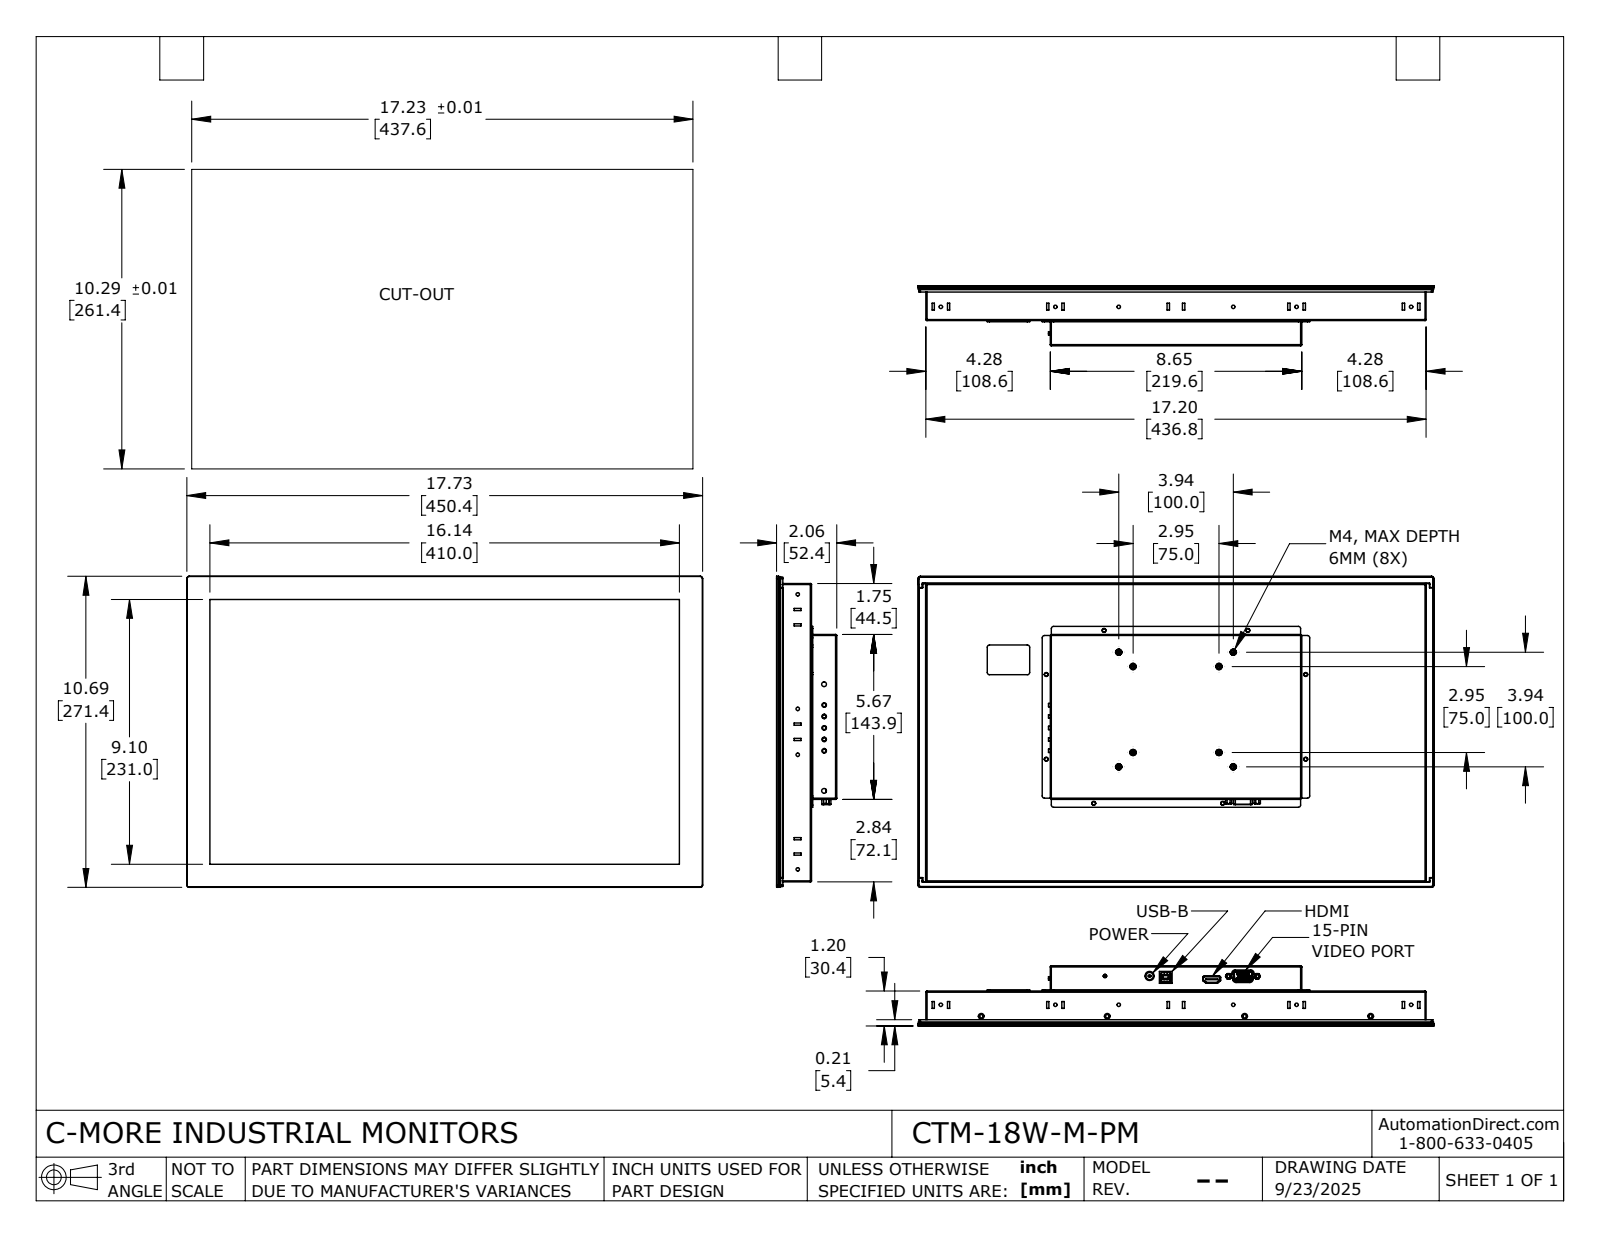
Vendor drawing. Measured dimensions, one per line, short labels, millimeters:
name: CTM-18W-M-PM-20250528_REV5
written by: SolidWorks 2024 (AUTOMOTIVE_DESIGN)
unit: mm
bodies: 1 solid, 945 faces (617 planar, 248 cylindrical, 80 other)
size: 450.4 × 271.4 × 52.5
volume: 4 174 000 mm³; area: 347 400 mm²
holes: 19× ⌀3, 15× ⌀1.2, 8× ⌀3.2, 8× ⌀3.5, 6× ⌀4.2, 5× ⌀4, 2× ⌀2.7, 1× ⌀2.5, 1× ⌀6.3, 1× ⌀8
bosses: 5× ⌀3, 1× ⌀2.4
rounds: 39× R2, 14× R1, 12× R3, 6× R1.2, 6× R1.3, 4× R0.4, 4× R0.7, 4× R0.9
face distances: 30.3, 22, 52.2, 52.5, 30.4, 1, 1.8, 260.5, 50.6, 28.7
hole spacings: 2.3, 6, 4, 2.3, 100, 4.6, 4.6, 88.4
